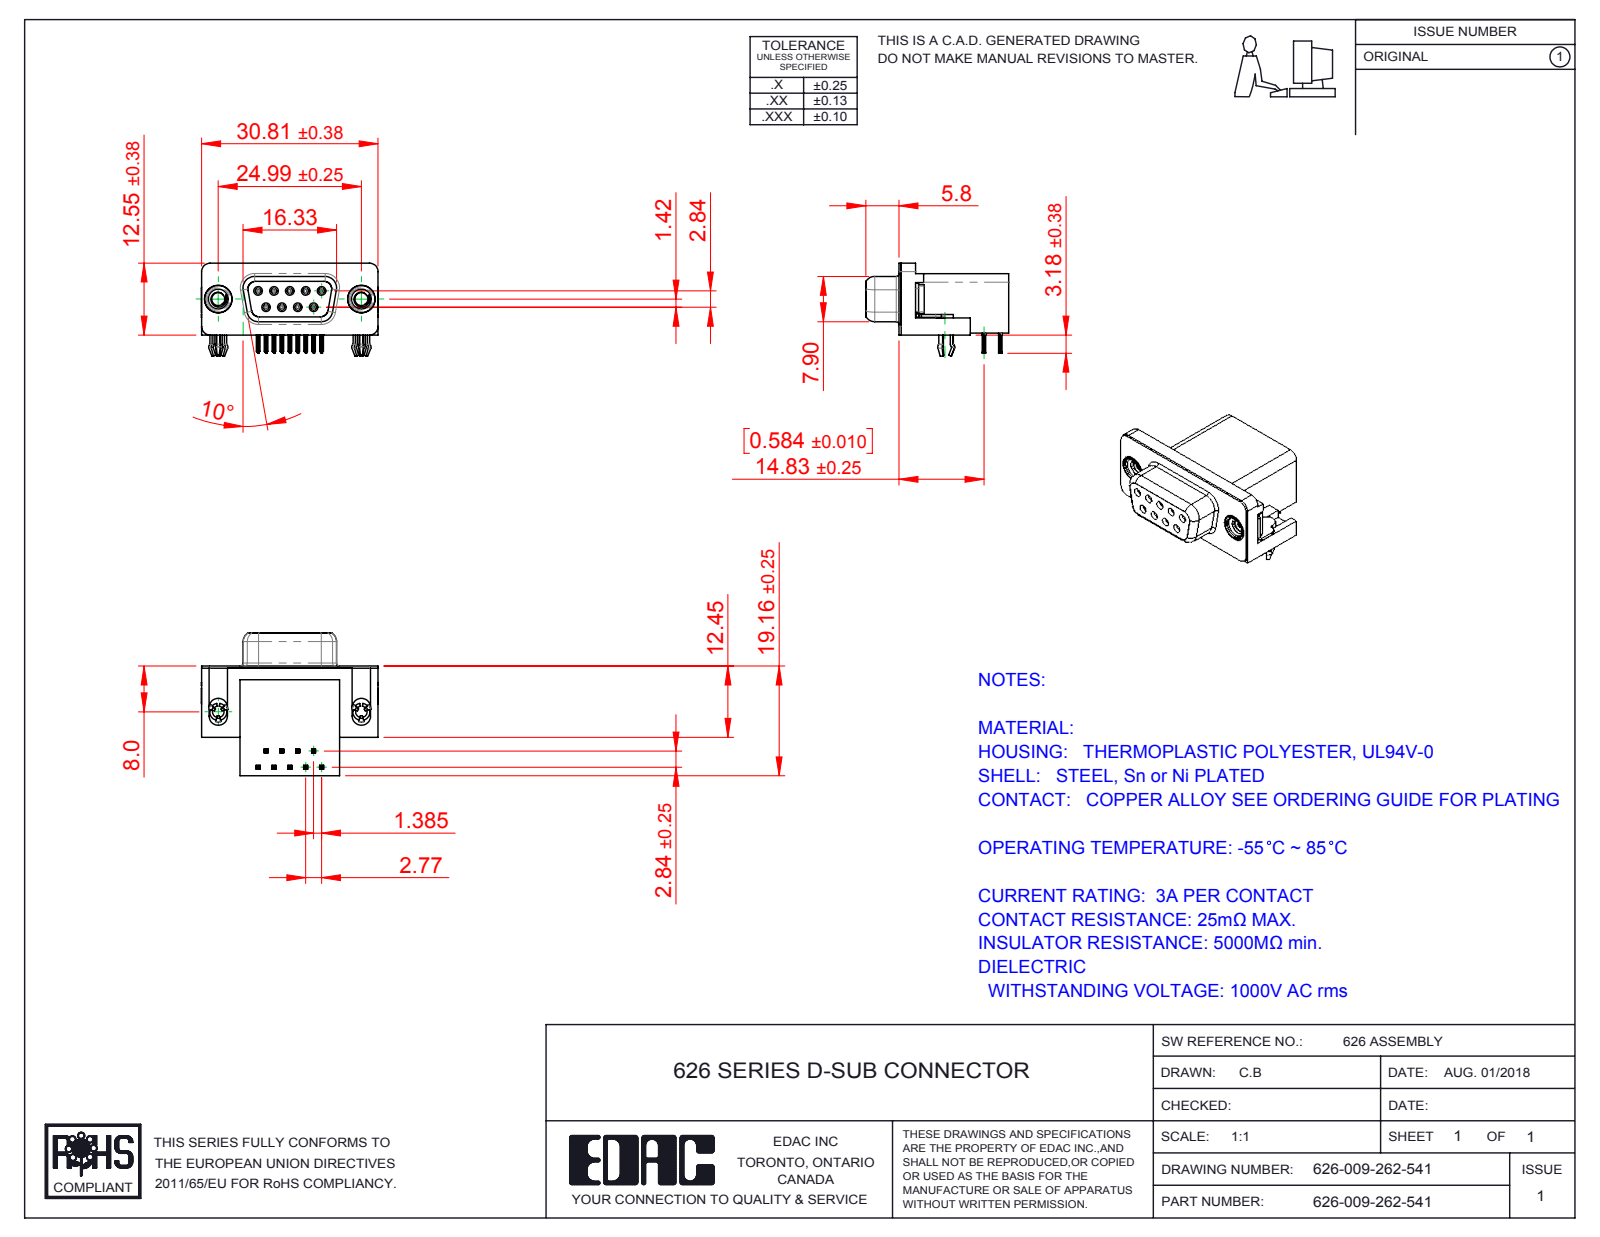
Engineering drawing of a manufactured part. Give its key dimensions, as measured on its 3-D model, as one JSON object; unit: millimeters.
{"part_name": "626 Shell_9 Socket; 626 Housing_9 Socket; 626 3 Prong Board Lock; 626-009-262-541 (+3 more)", "step_written_by": "SolidWorks 2016 (CONFIG_CONTROL_DESIGN)", "units": "millimeters", "bodies": {"solids": 15, "faces": 1676, "planar": 722, "cylindrical": 422, "other": 532}, "overall_size": [30.89, 24.96, 16.25], "volume_mm3": 4978, "surface_area_mm2": 5852, "round_holes": [[0.8, 9], [0.9, 9], [2, 2], [2.26, 2], [4, 2], [4.8, 2], [5, 2]], "round_bosses_or_shafts": [[1.2, 9], [4.9, 2], [4.75, 2], [3.9, 2], [3, 2]], "partial_cylinders_radius": [[0.1, 72], [0.15, 36], [0.35, 18], [1, 18], [0.25, 12], [0.34, 9], [1.35, 8], [1.6, 8]], "face_to_face_distances": [0.4, 10.34, 0.35, 18.76, 19.16, 2.9, 2.5, 6.2, 16.26, 10.69], "hole_center_spacings": [3.16, 2.77, 5.54, 5.03, 5.04, 8.31, 7.48, 7.49]}
